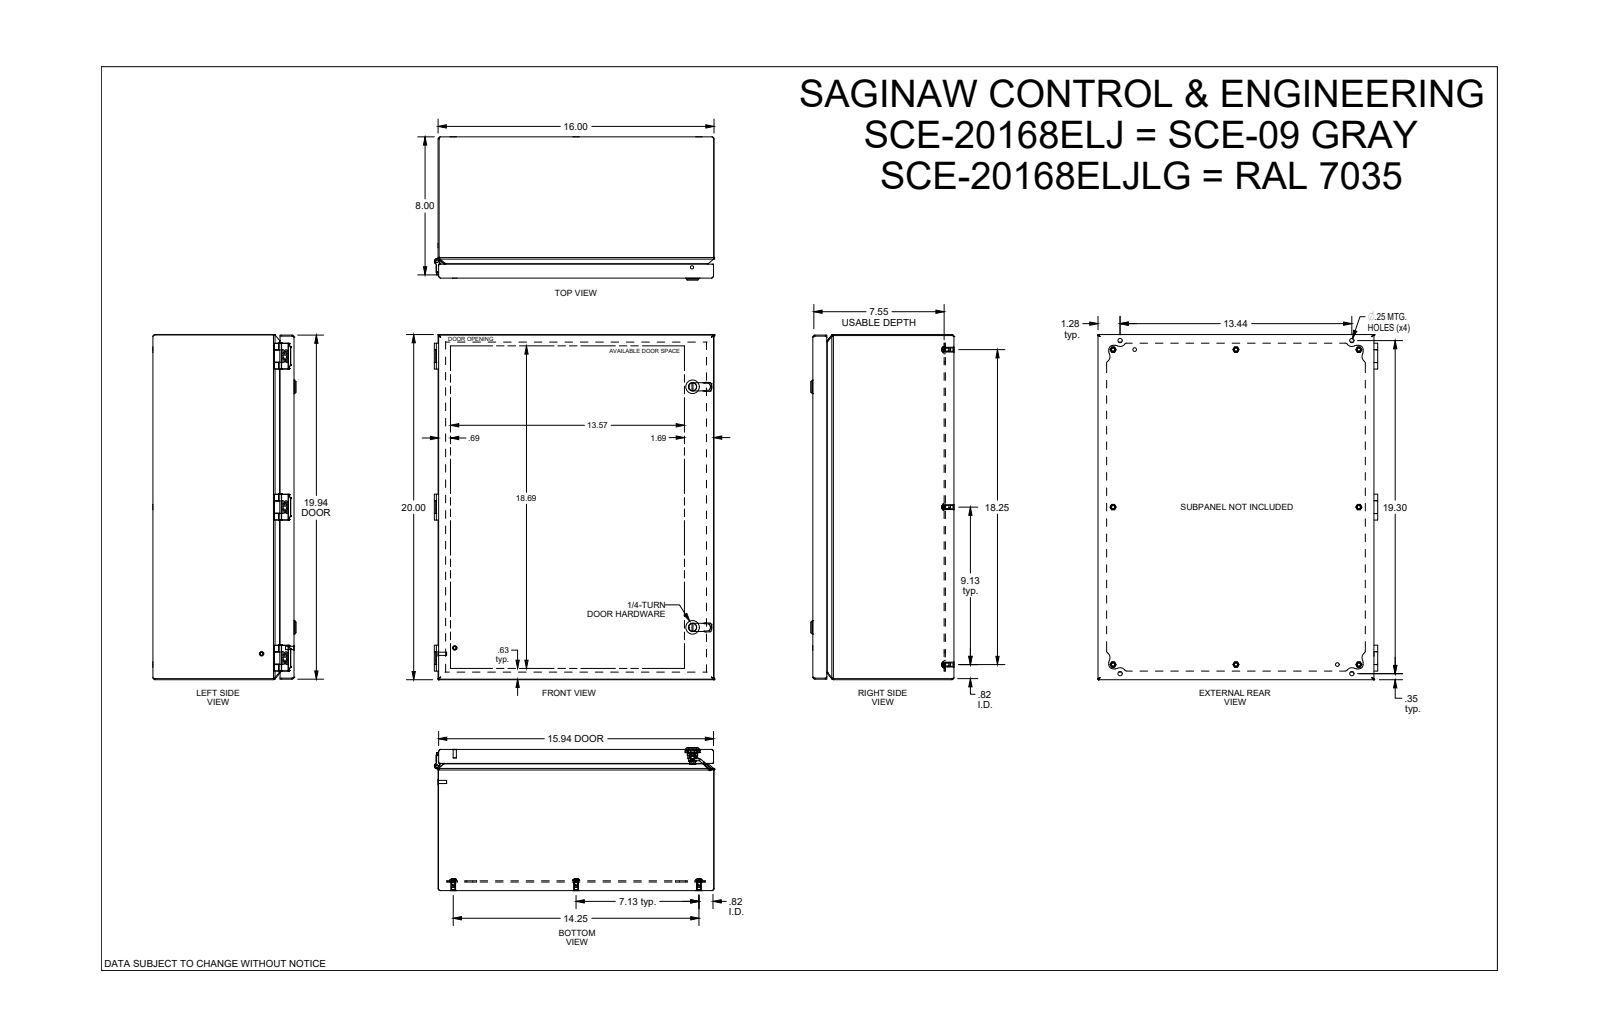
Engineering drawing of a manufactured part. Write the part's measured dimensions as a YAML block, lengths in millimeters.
part_name: "SCE-20168ELJ"
step_written_by: "SolidWorks 2021 (AUTOMOTIVE_DESIGN)"
units: millimeters
bodies: {solids: 36, faces: 2036, planar: 647, cylindrical: 579, other: 810}
overall_size: [508, 412, 210.6]
volume: 1612000
surface_area: 2030000
round_holes:
  - {diameter: 6.4, count: 8}
  - {diameter: 7.2, count: 6}
  - {diameter: 4.3, count: 3}
  - {diameter: 5.1, count: 2}
  - {diameter: 5.5, count: 2}
  - {diameter: 6.1, count: 2}
  - {diameter: 6.5, count: 2}
  - {diameter: 6.8, count: 2}
  - {diameter: 7.2, count: 2}
  - {diameter: 8.3, count: 2}
  - {diameter: 12.1, count: 2}
  - {diameter: 16, count: 2}
round_bosses_or_shafts:
  - {diameter: 4.8, count: 9}
  - {diameter: 9.5, count: 8}
  - {diameter: 12.2, count: 3}
  - {diameter: 6.6, count: 3}
  - {diameter: 2.5, count: 3}
  - {diameter: 0.5, count: 3}
  - {diameter: 20, count: 2}
  - {diameter: 13.9, count: 2}
partial_cylinders:
  - {radius: 2.7, count: 99}
  - {radius: 0.1, count: 54}
  - {radius: 0.2, count: 48}
  - {radius: 0.3, count: 31}
  - {radius: 0.3, count: 18}
  - {radius: 0.6, count: 18}
  - {radius: 1.3, count: 16}
  - {radius: 1.6, count: 12}
face_to_face_distances: [1.5, 1.6, 207.9, 206.4, 206.3, 204.8, 14.5, 13, 191.8, 193.4]
hole_center_spacings: [181, 181, 497.7, 149.2, 231.8, 294.1, 362, 429.8]
